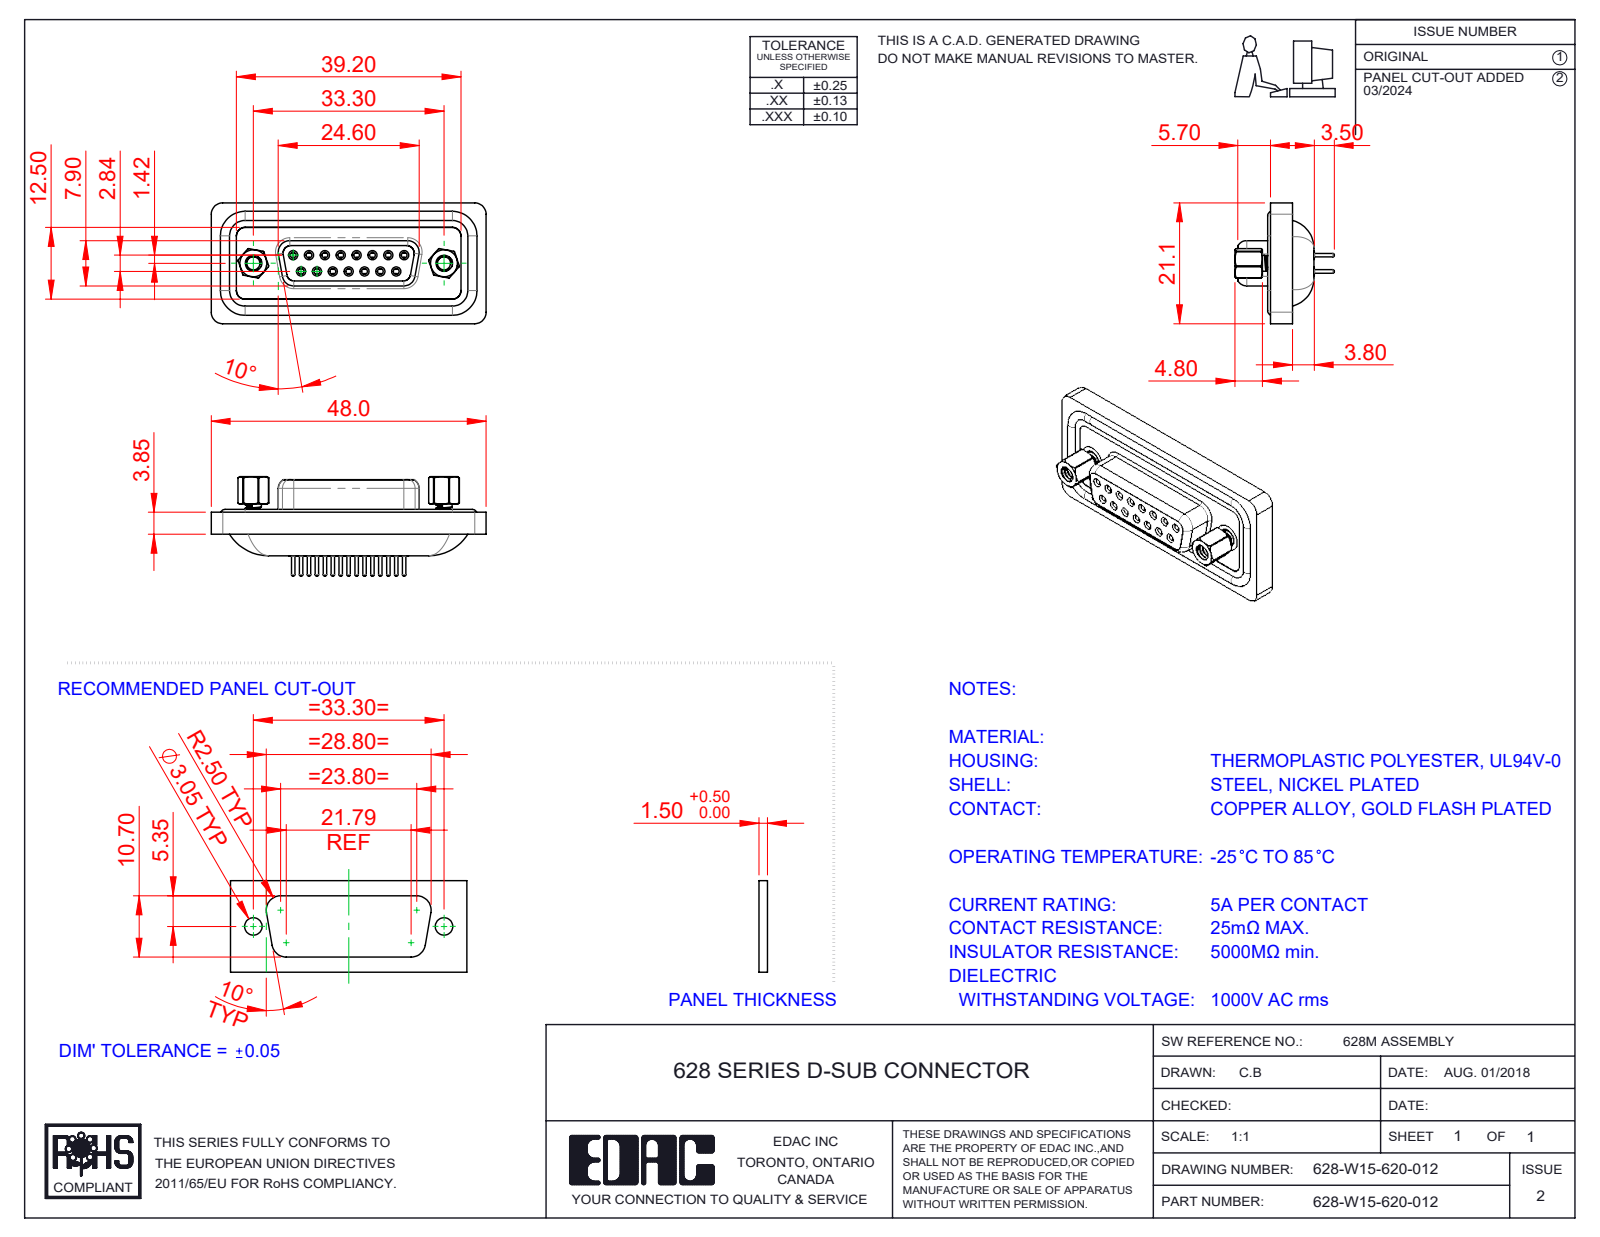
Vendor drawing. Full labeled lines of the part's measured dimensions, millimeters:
Part name (STEP PRODUCT): 628W 4-40 Threaded Rivet; 628W Waterproof Housing_15 Contacts; 628W 4-40 Hex Standoff; 628-W15-620-012 (+4 more)
STEP written by: SolidWorks 2020 (CONFIG_CONTROL_DESIGN)
Units: millimetres
Bodies: 23 solids, 1278 faces (326 planar, 535 cylindrical, 417 other)
Overall size (bounding box): 48 × 21.1 × 16.85
Volume: 6 367 mm³ · Surface area: 9 662 mm²
Round holes (diameter × count): ⌀1 ×15, ⌀1.1 ×15, ⌀1.5 ×15, ⌀1.7 ×15, ⌀1.8 ×15, ⌀2 ×15, ⌀2.26 ×2, ⌀2.29 ×2, ⌀4 ×2, ⌀4.8 ×2, ⌀5 ×2
Round bosses / shafts (diameter × count): ⌀1.6 ×19, ⌀2.2 ×15, ⌀0.6 ×15, ⌀1.5 ×7, ⌀4.9 ×2, ⌀2.79 ×2
Partial cylindrical surfaces — rounded edges, fillets, slot ends (radius × count): R2 ×16, R1.5 ×14, R1.35 ×8, R2.7 ×6, R0.5 ×4, R0.9 ×4, R1.6 ×4, R1.75 ×4
Main face-to-face distances: 0.4, 1.1, 2.75, 0.5, 3.75, 7.45, 7.5, 1, 13.65, 8.45
Hole centre spacings: 3.16, 2.77, 5.54, 8.31, 5.03, 5.04, 7.48, 7.49
